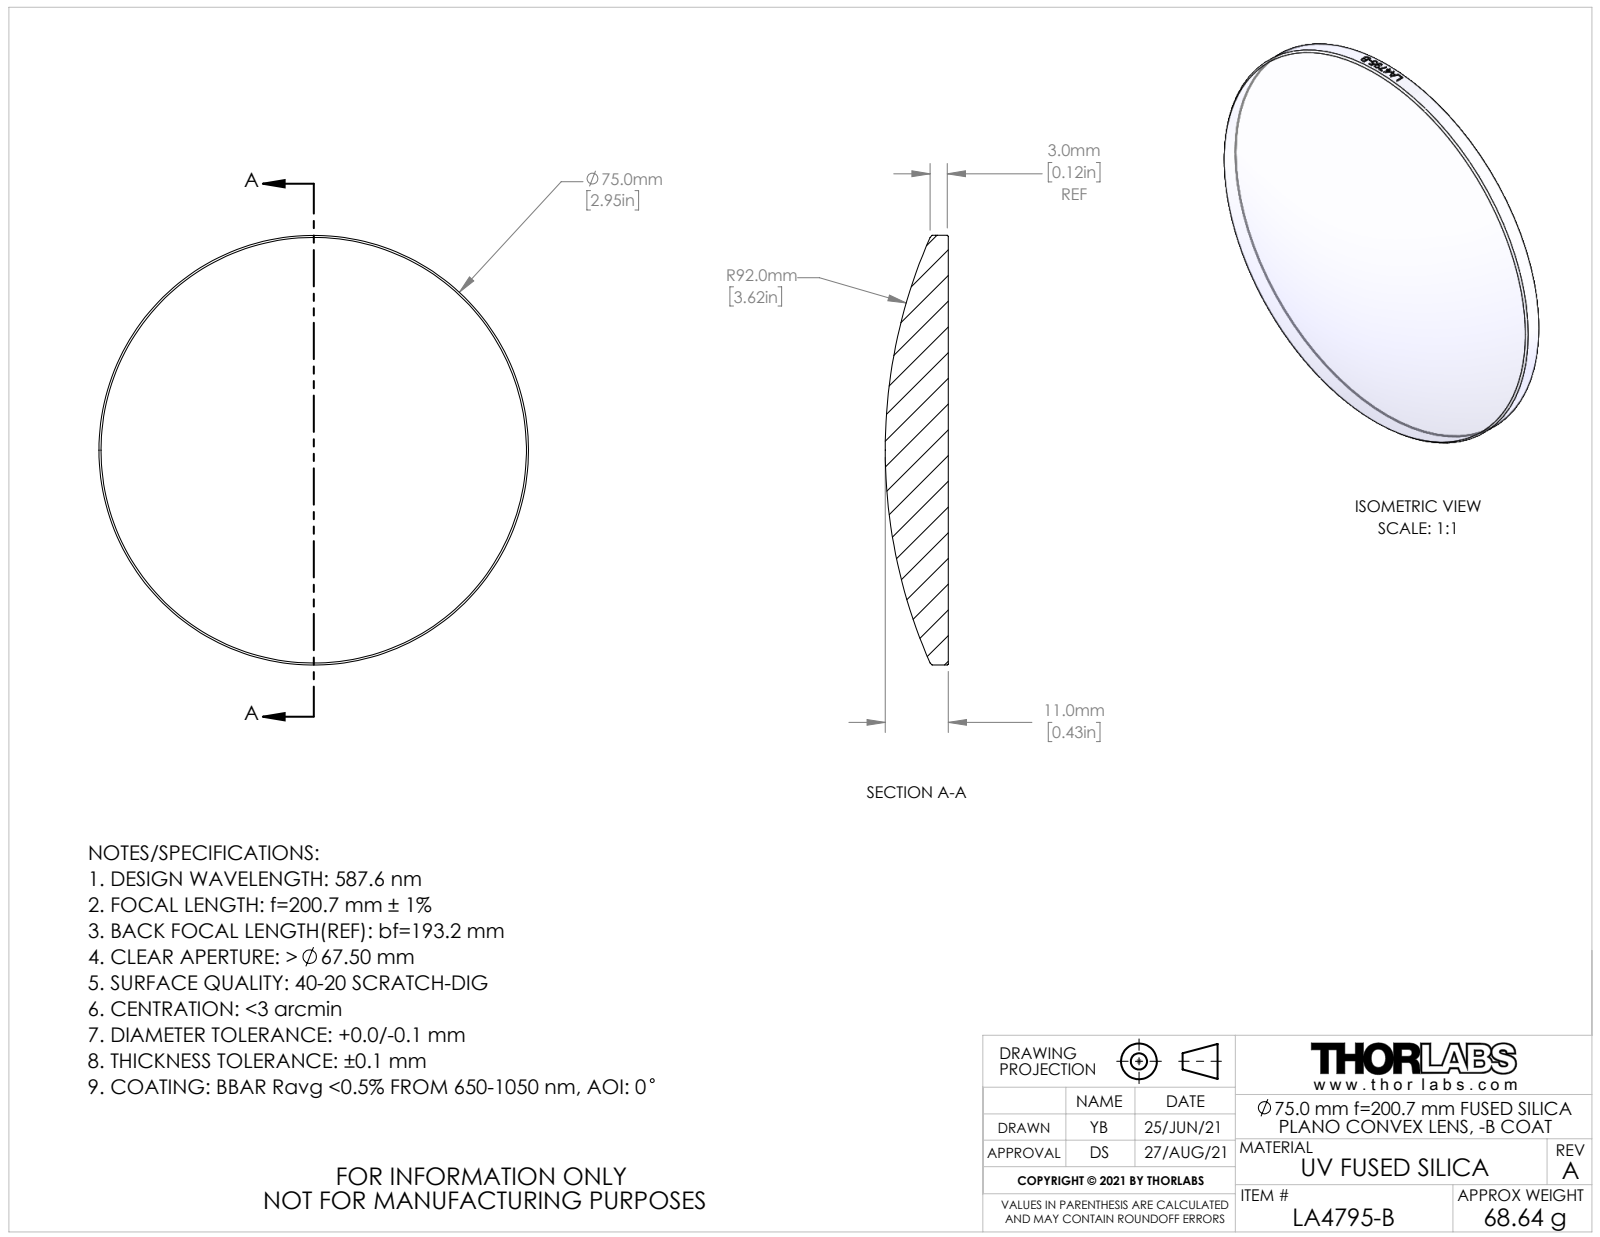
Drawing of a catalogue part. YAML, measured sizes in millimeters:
part_name: "CTN017915-E0W"
step_written_by: "SolidWorks 2018 (AUTOMOTIVE_DESIGN)"
units: millimeters
bodies: {solids: 1, faces: 22, planar: 1, cylindrical: 15, other: 6}
overall_size: [75, 75, 10.99]
volume: 31157
surface_area: 9702
round_bosses_or_shafts:
  - {diameter: 75, count: 1}
